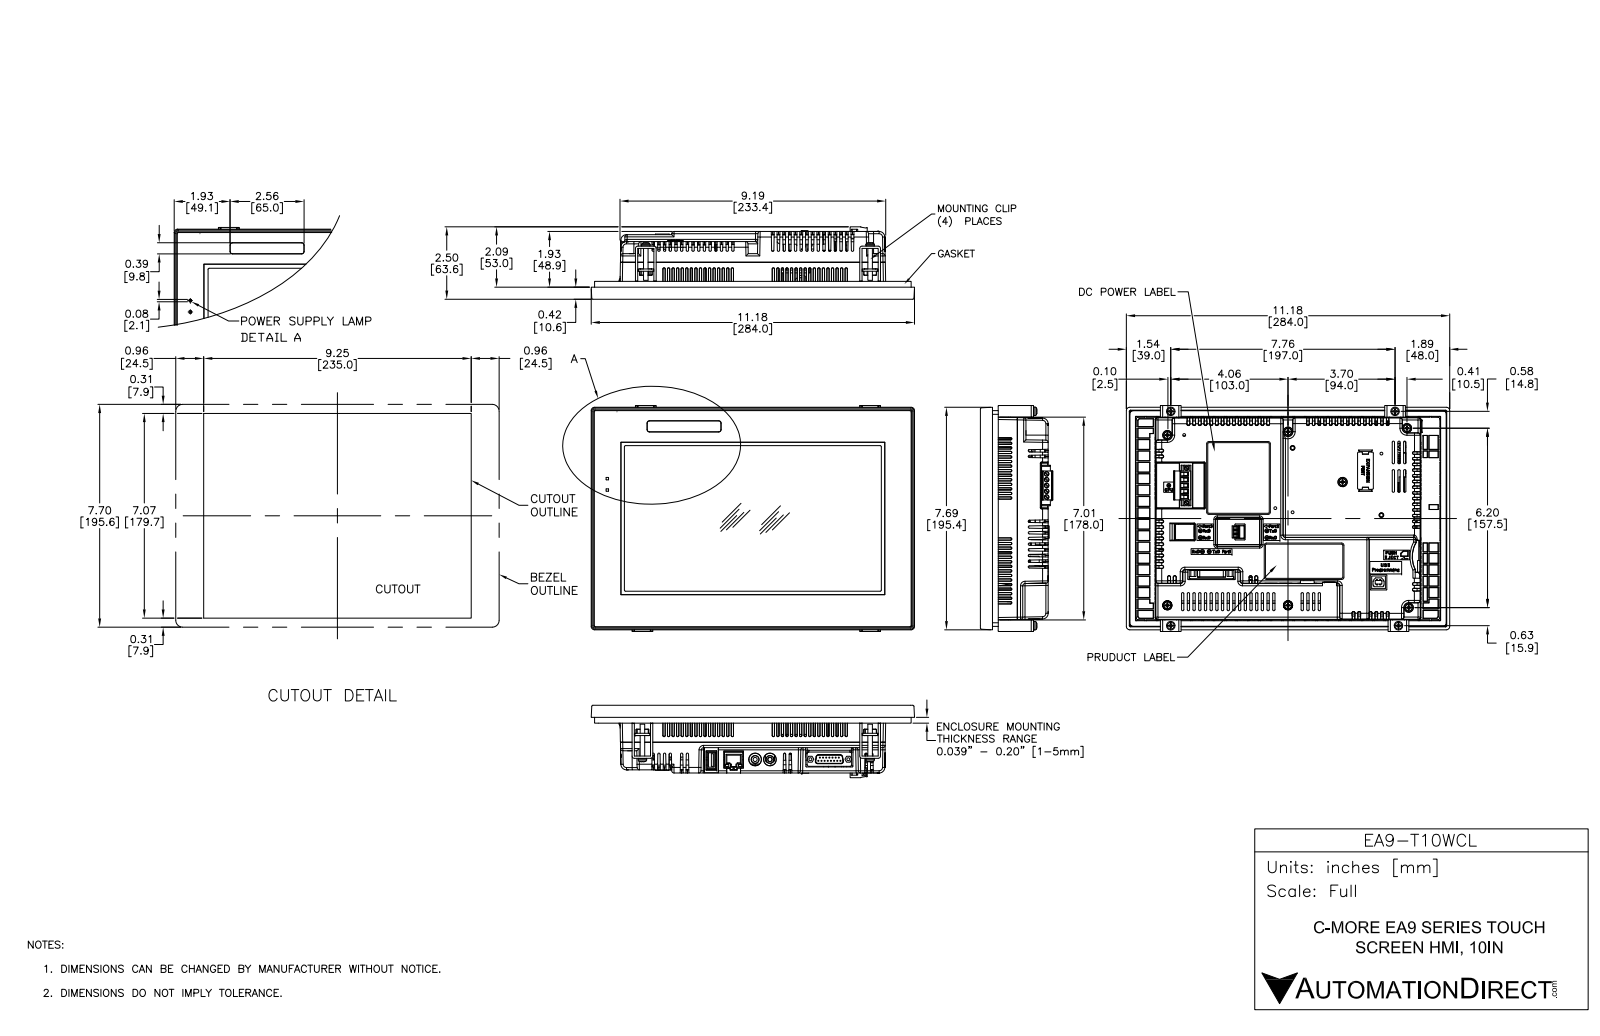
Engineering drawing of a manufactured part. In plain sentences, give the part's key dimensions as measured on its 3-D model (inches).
The part is named "OverlaySheet-10W; EA9-T10WCL_outline_M1; EA9-T10WCL_outline_M2; EA9-T10WCL_outline_M3 (+5 more)". Its 3-D file was written by "SolidWorks 2017 (AUTOMOTIVE_DESIGN)". It is 8 solids with 6953 faces: 5392 planar, 1017 cylindrical and 544 other. Overall it measures 11.181 by 7.811 by 2.504 inches. Its volume is 139.1 cubic inches and its surface area 597.1 square inches. Round holes: 15 of diameter 0.039, 9 of diameter 0.157, 7 of diameter 0.024, 7 of diameter 0.138, 7 of diameter 0.197, 4 of diameter 0.098, 3 of diameter 0.114, 2 of diameter 0.071, 2 of diameter 0.102, 2 of diameter 0.12, 2 of diameter 0.142, 2 of diameter 0.154. Round bosses or shafts: 7 of diameter 0.248, 7 of diameter 0.118, 6 of diameter 0.043, 5 of diameter 0.149, 4 of diameter 0.294, 4 of diameter 0.098, 3 of diameter 0.11, 3 of diameter 0.047. Partial cylindrical surfaces (rounded edges, fillets, slot ends): 150 of radius 0.039, 90 of radius 0.02, 87 of radius 0.079, 64 of radius 0.049, 58 of radius 0.043, 36 of radius 0.008, 28 of radius 0.031, 25 of radius 0.059. The main face-to-face distances are 0.197, 0.104, 0.112, 1.978, 1.986, 1.874, 0.35, 2.336, 2.329, 2.224. The hole center spacings are 0.125, 0.109, 0.218, 0.327, 0.198, 0.198, 0.236, 0.436.
